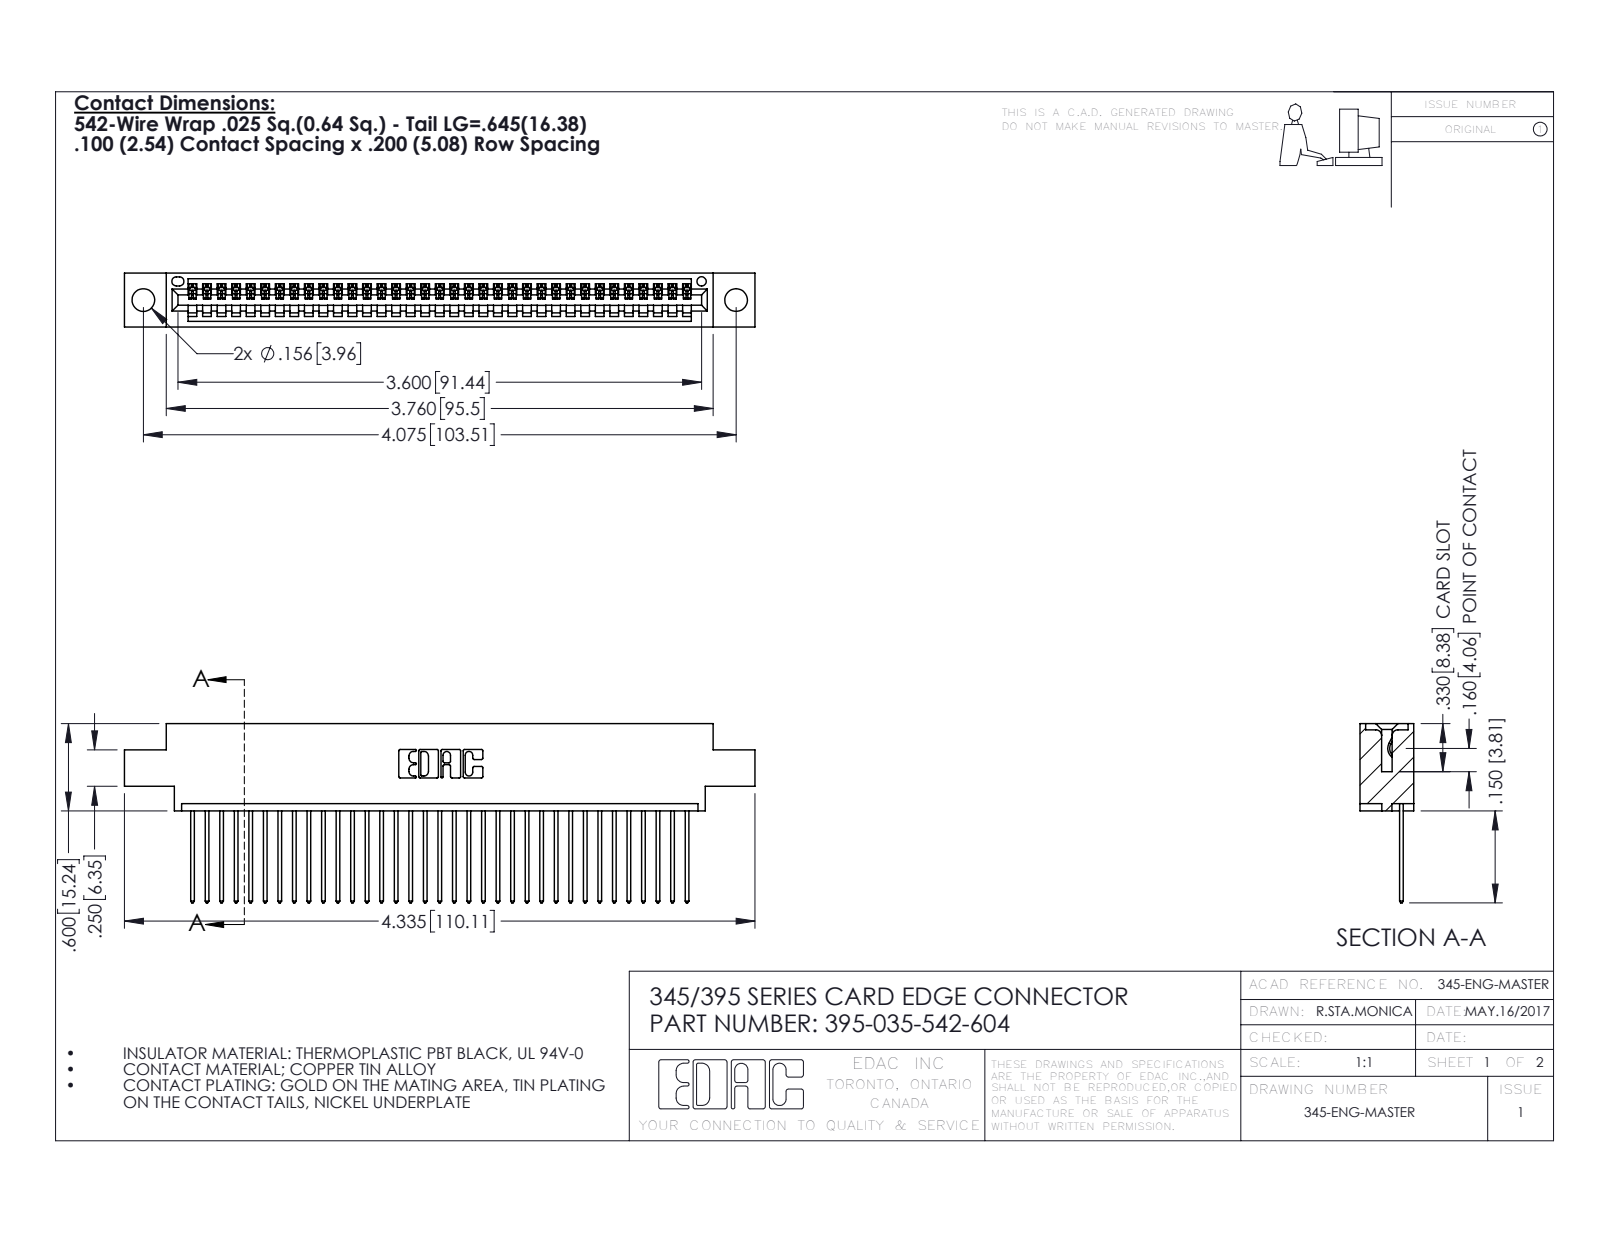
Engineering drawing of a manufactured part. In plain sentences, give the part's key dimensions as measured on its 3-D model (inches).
The part is named "395-035-542-604; 345 Part_0.170 Offset - 0.156 Dia-TH; 345-292-001_345-293-142". Its 3-D file was written by "SolidWorks 2016 (CONFIG_CONTROL_DESIGN)". It is 36 solids with 2160 faces: 1484 planar, 676 cylindrical and 0 other. Overall it measures 4.335 by 1.232 by 0.37 inches. Its volume is 0.627 cubic inches and its surface area 21.69 square inches. Round holes: 2 of diameter 0.156, 1 of diameter 0.064. Partial cylindrical surfaces (rounded edges, fillets, slot ends): 70 of radius 0.006, 70 of radius 0.01, 22 of radius 0.01, 6 of radius 0.007, 6 of radius 0.031, 3 of radius 0.026, 2 of radius 0.031, 2 of radius 0.04. The main face-to-face distances are 0.298, 0.072, 0.37, 0.098, 0.272, 0.025, 0.2, 0.225, 0.175, 0.149. The hole center spacings are 0.27, 3.839, 4.075.
